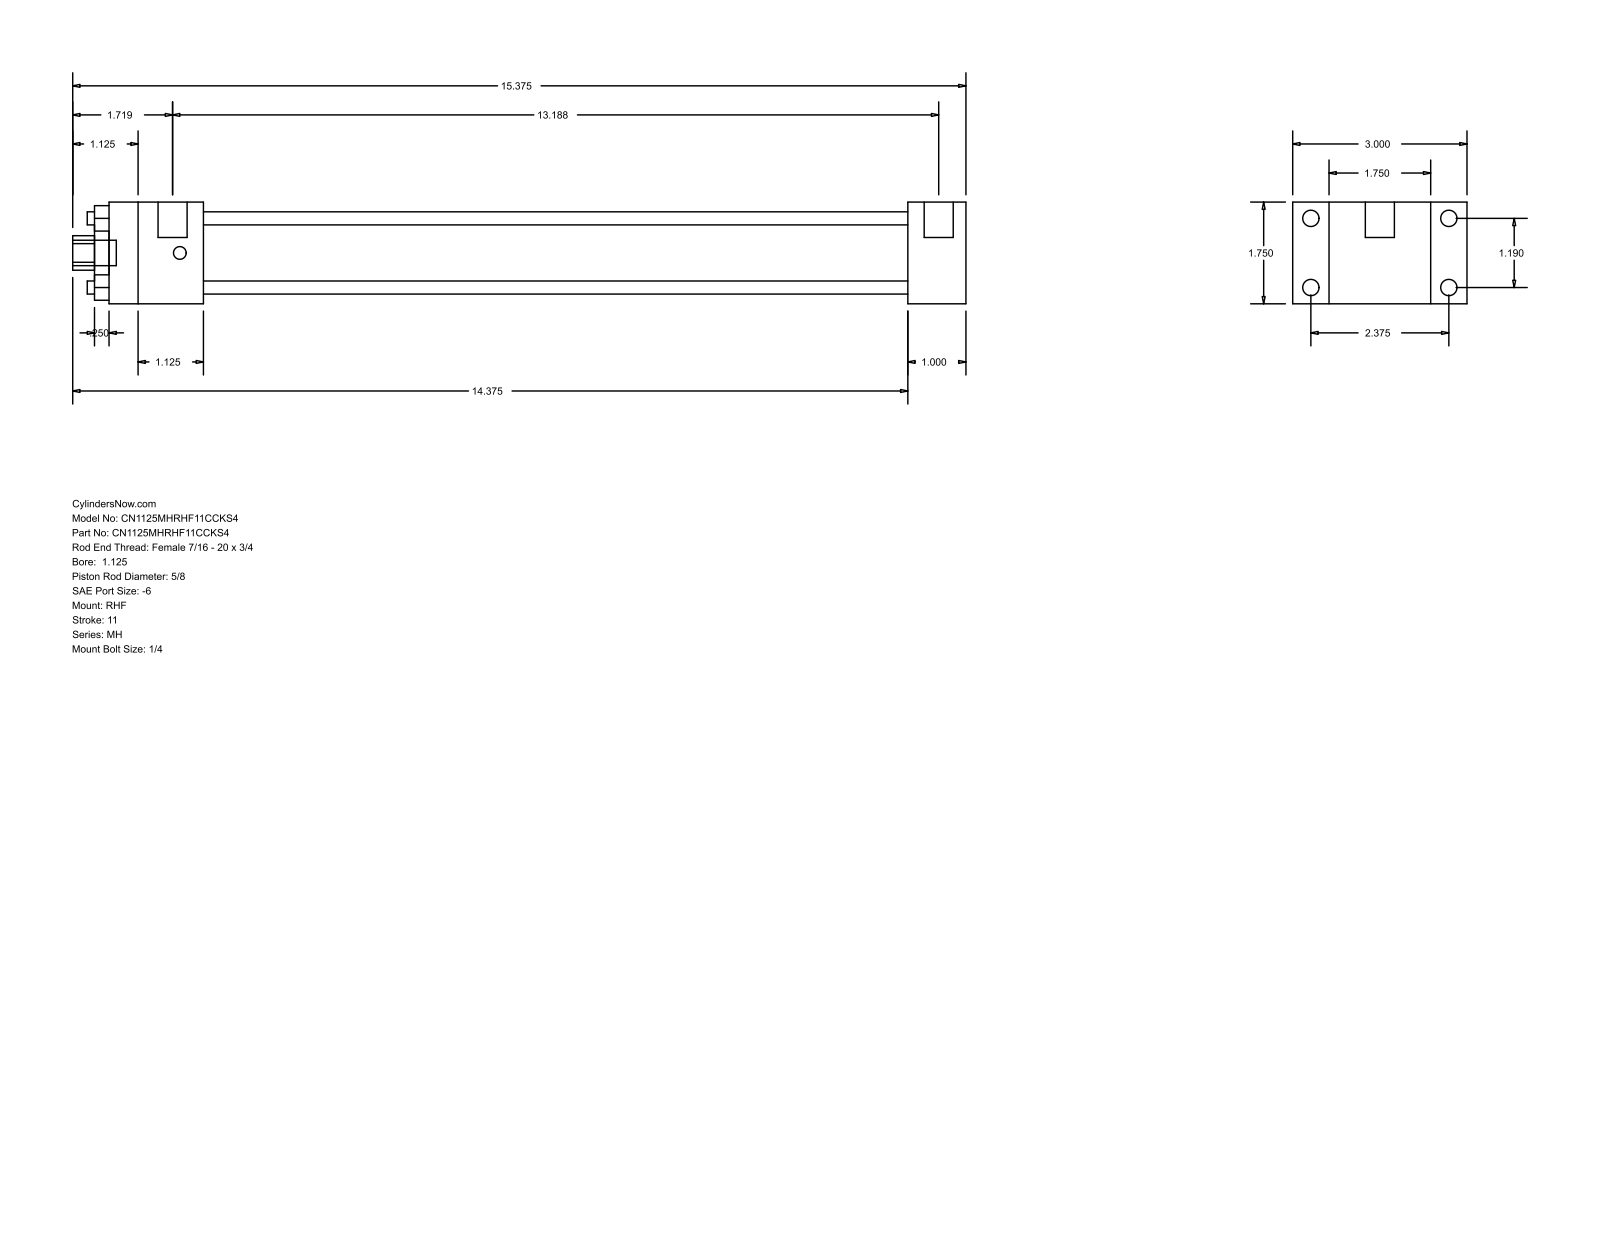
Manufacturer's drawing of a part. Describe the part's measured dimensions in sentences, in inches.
The part is named "MH_RHF__0112_0.625". Its 3-D file was written by "GSSL Pune (CONFIG_CONTROL_DESIGN)". It is 0 solids with 88 faces: 60 planar, 28 cylindrical and 0 other. Overall it measures 15.375 by 3 by 1.75 inches. Round holes: 4 of diameter 0.225, 1 of diameter 0.625, 1 of diameter 1.125, 1 of diameter 1.375. Round bosses or shafts: 4 of diameter 0.281, 4 of diameter 0.219, 2 of diameter 0.5, 1 of diameter 0.437. Partial cylindrical surfaces (rounded edges, fillets, slot ends): 1 of radius 0.297. The main face-to-face distances are 1.75, 0.625, 2.375, 1, 3, 12.125, 13.125, 1.625, 13.75, 14.75. The hole center spacings are 0.841, 1.19, 1.683.
